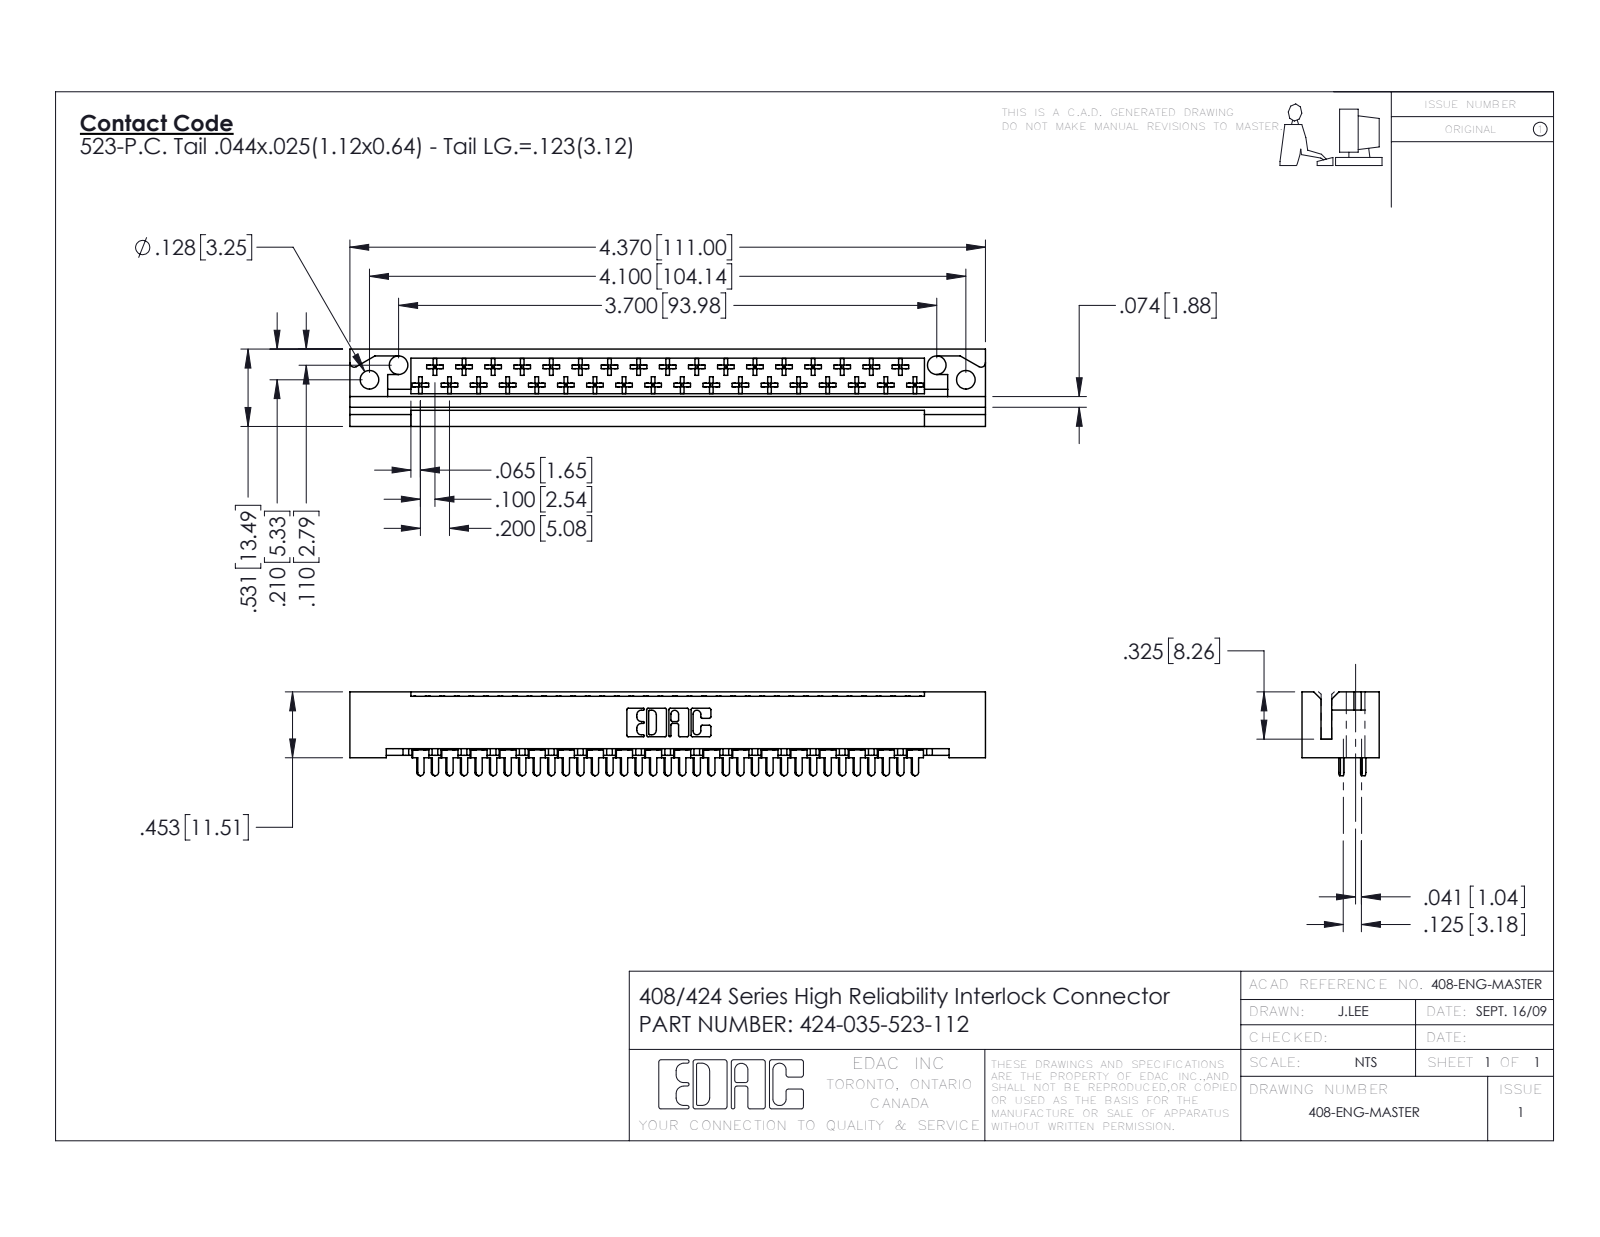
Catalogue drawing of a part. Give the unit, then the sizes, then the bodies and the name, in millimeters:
Units: millimetres
Overall size (bounding box): 111 × 14.6 × 13.5
Round holes (diameter × count): ⌀3.3 ×4
Partial cylindrical surfaces — rounded edges, fillets, slot ends (radius × count): R0.3 ×210, R0.5 ×37, R0.6 ×35, R0.3 ×22, R0.2 ×6, R0.8 ×6, R0.7 ×3, R0.8 ×2
Main face-to-face distances: 0.6, 13.5, 10.2, 3.2, 2.5, 5.5, 6.9, 6, 6.6, 0.6
Hole centre spacings: 5.7, 99.1, 94, 104.1
Volume: 12 100 mm³ · Surface area: 14 930 mm²
Bodies: 36 solids, 2070 faces (1559 planar, 371 cylindrical, 140 other)
Part name (STEP PRODUCT): 408-290-001_408-290-123 - Top; 424-035-523-112; 408-290-001_408-290-123 - Bottom; 424 Part_035
STEP written by: SolidWorks 2016 (CONFIG_CONTROL_DESIGN)
